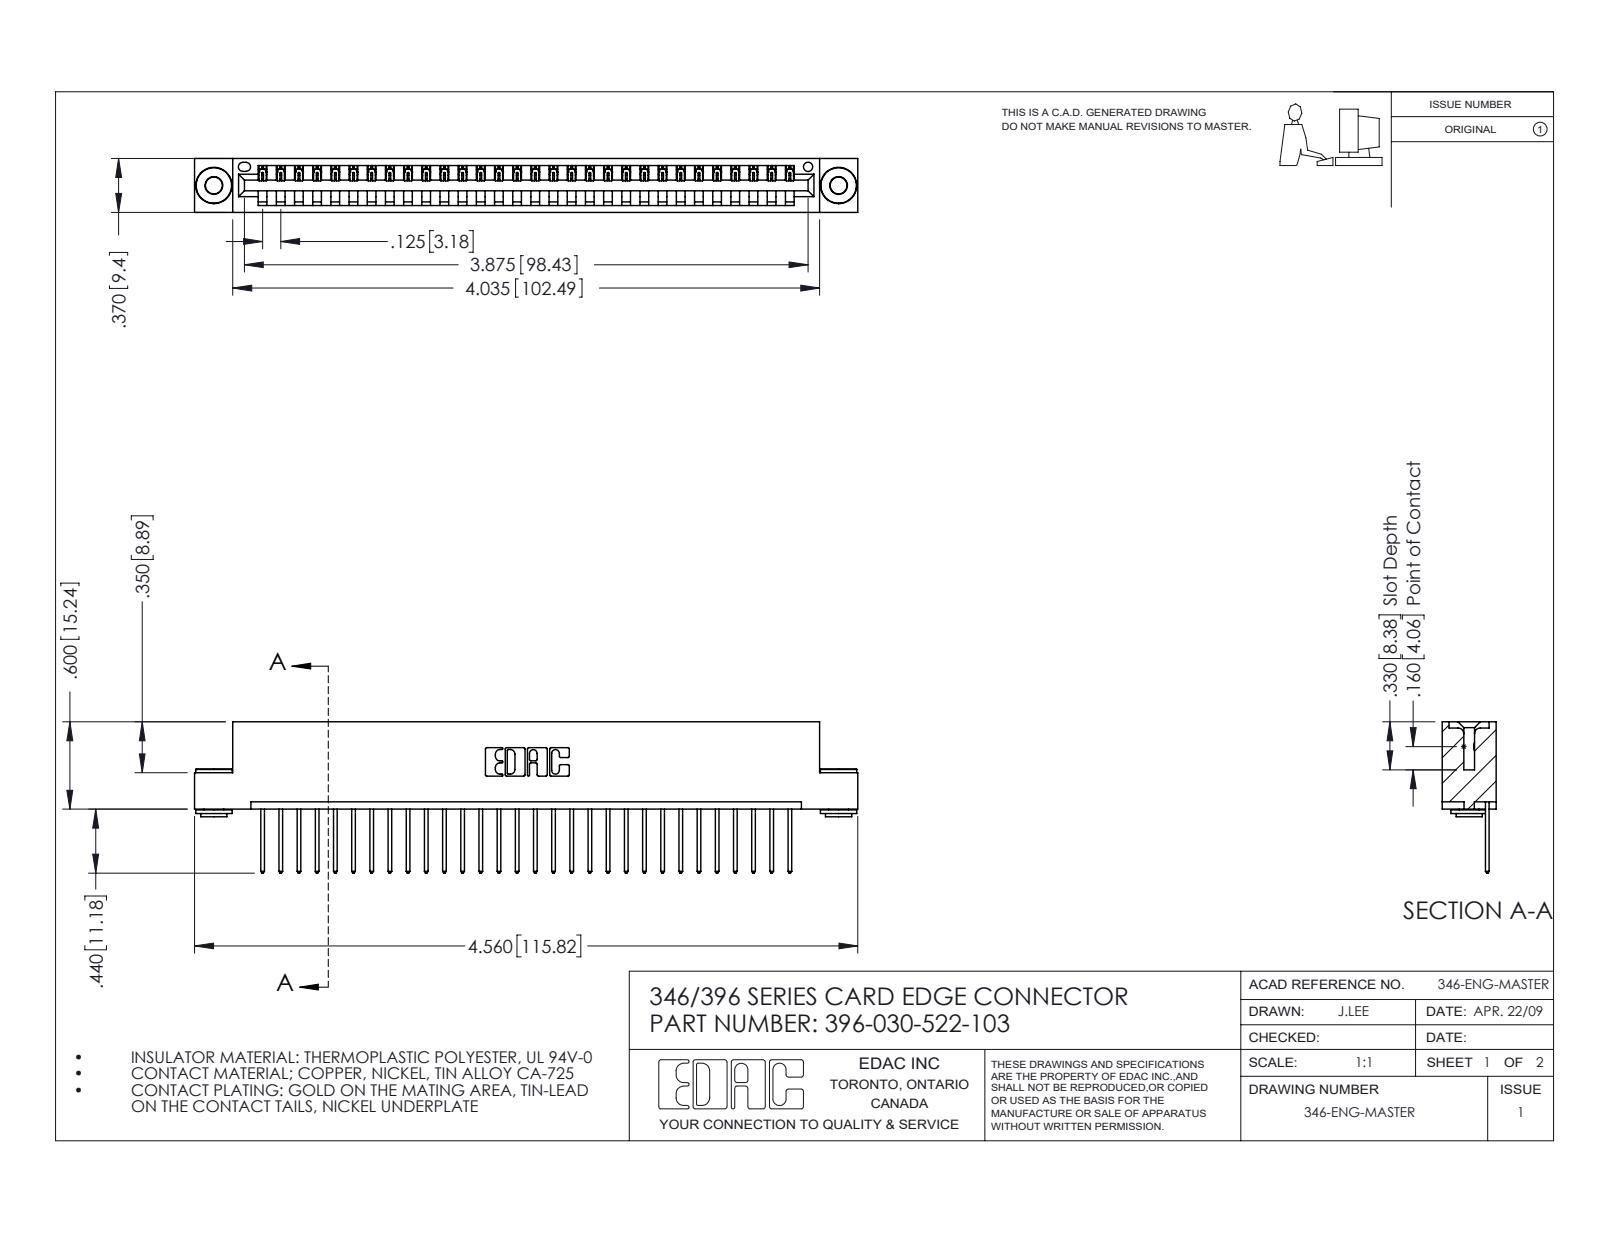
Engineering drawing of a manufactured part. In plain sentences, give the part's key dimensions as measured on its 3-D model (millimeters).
The part is named "345-250-002_345-250-002-102; 345-292-001_345-293-122; 346 Part_Flush Mounting Lugs - 0.156 Dia-TH; 396-030-522-103". Its 3-D file was written by "SolidWorks 2016 (CONFIG_CONTROL_DESIGN)". It is 33 solids with 1900 faces: 1286 planar, 606 cylindrical and 8 other. Overall it measures 115.8 by 26.4 by 9.4 millimeters. Its volume is 11 000 cubic millimeters and its surface area 13 980 square millimeters. Round holes: 2 of diameter 2.9, 2 of diameter 4, 1 of diameter 1.6. Round bosses or shafts: 2 of diameter 6.4, 2 of diameter 4.6, 2 of diameter 3.5. Partial cylindrical surfaces (rounded edges, fillets, slot ends): 60 of radius 0.2, 60 of radius 0.3, 22 of radius 0.3, 6 of radius 0.2, 6 of radius 0.8, 3 of radius 0.7, 2 of radius 0.8, 2 of radius 1. The main face-to-face distances are 1.2, 8.2, 6.4, 9.4, 0.6, 1.8, 7.6, 3.8, 5.6, 2.5. The hole center spacings are 6.2, 103.8, 109.1.
